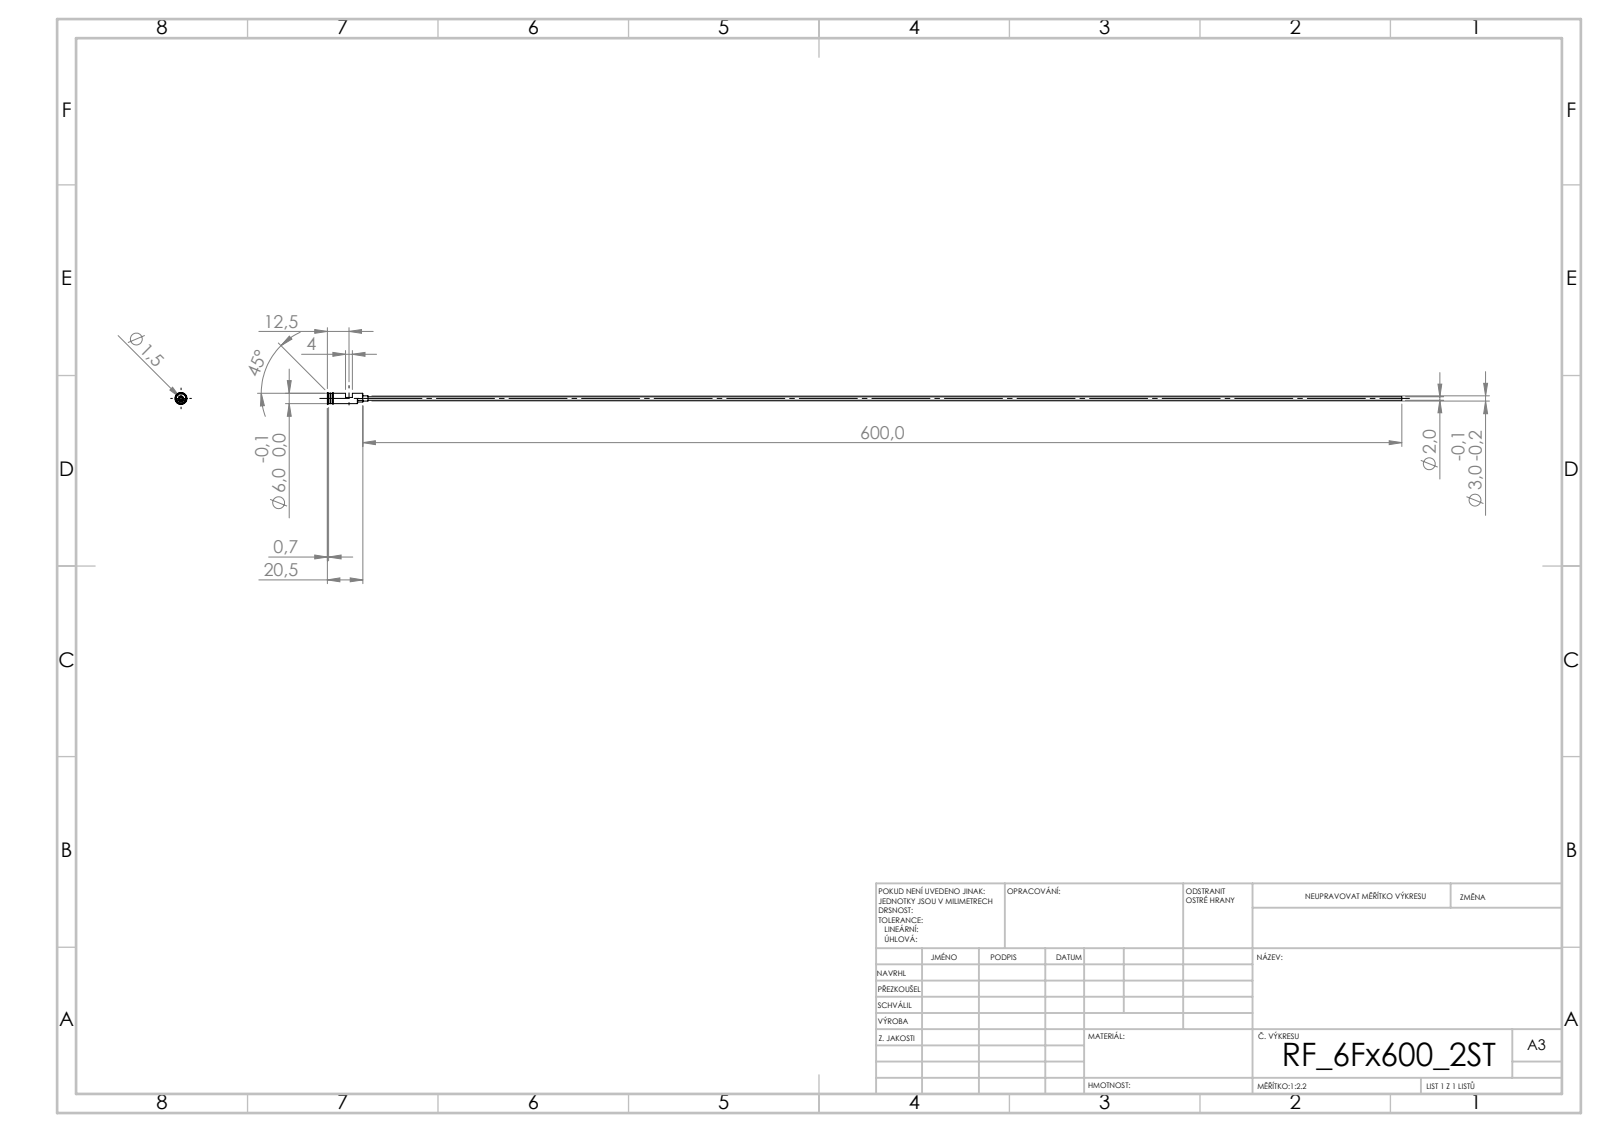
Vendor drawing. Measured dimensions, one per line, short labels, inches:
written by: SolidWorks 2019 (CONFIG_CONTROL_DESIGN)
unit: in
bodies: 1 solid, 55 faces (24 planar, 19 cylindrical, 12 other)
size: 24.429 × 0.276 × 0.276
volume: 0.081 in³; area: 11.06 in²
holes: 1× ⌀0.059
bosses: 1× ⌀0.276, 1× ⌀0.236, 1× ⌀0.228, 1× ⌀0.118, 1× ⌀0.079
rounds: 2× R0.118, 1× R0.081
face distances: 0.118, 0.236, 0.807, 0.394, 0.413, 0.571, 0.157, 0.079, 0.276, 0.689
